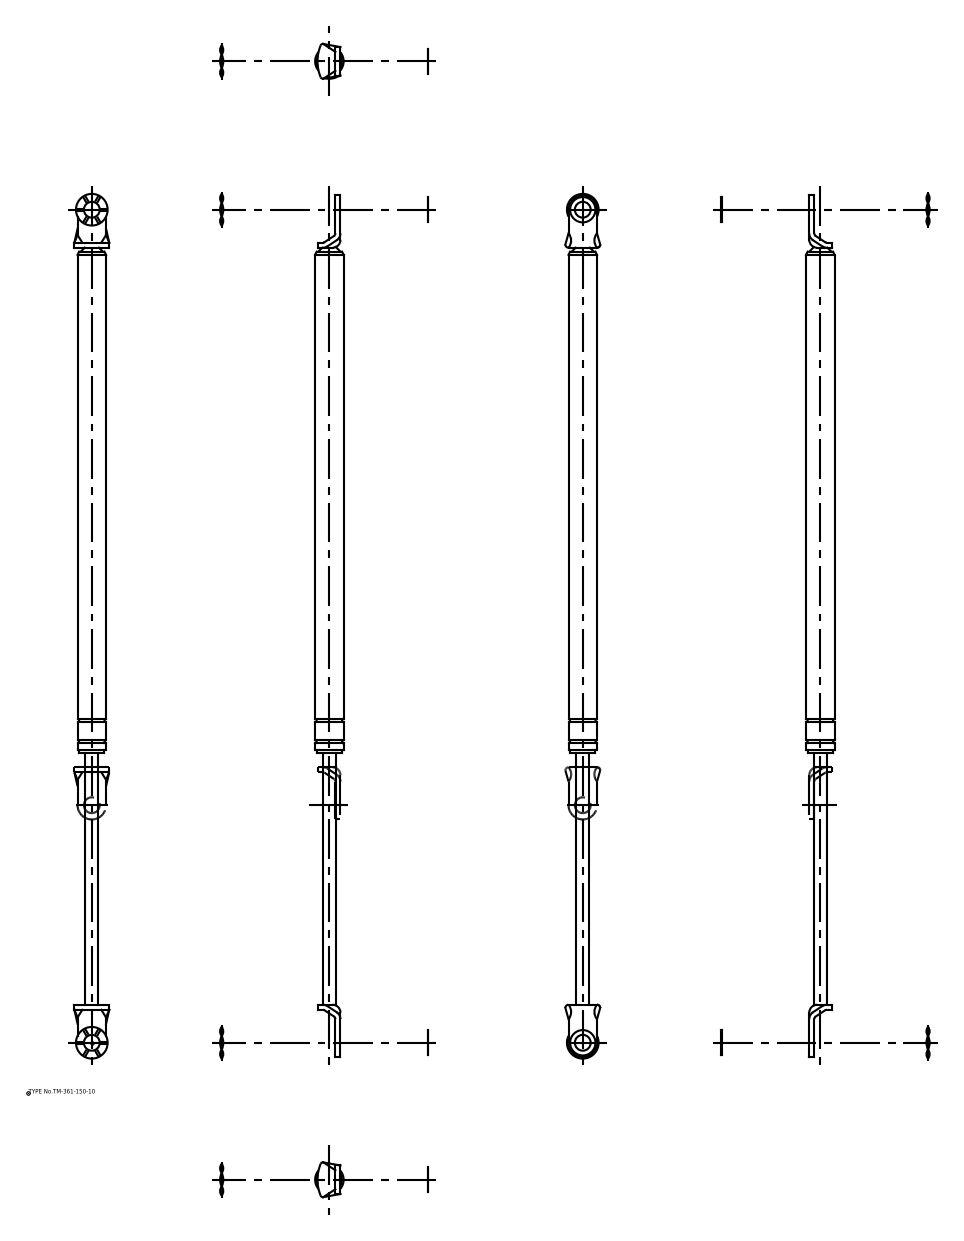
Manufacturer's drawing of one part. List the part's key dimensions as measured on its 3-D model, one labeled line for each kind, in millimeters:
Part name (STEP PRODUCT): ウェーブワッシャー; ワッシャー; 本体; 本体_div
STEP written by: spGate 16.7.1 (AUTOMOTIVE_DESIGN)
Units: millimetres
Bodies: 6 solids, 94 faces (42 planar, 44 cylindrical, 8 other)
Overall size (bounding box): 546 × 22 × 18.5
Volume: 94 156 mm³ · Surface area: 28 048 mm²
Round holes (diameter × count): ⌀10 ×2
Round bosses / shafts (diameter × count): ⌀16 ×3, ⌀20 ×2, ⌀18.5 ×1, ⌀18 ×1, ⌀8 ×1
Partial cylindrical surfaces — rounded edges, fillets, slot ends (radius × count): R4.4 ×2, R5 ×2, R9 ×2, R26.32 ×1
Main face-to-face distances: 3.2, 2, 5.2, 481.2, 5.7, 3.7, 0.5, 322.2, 162.2, 484.4
Hole centre spacings: 526
